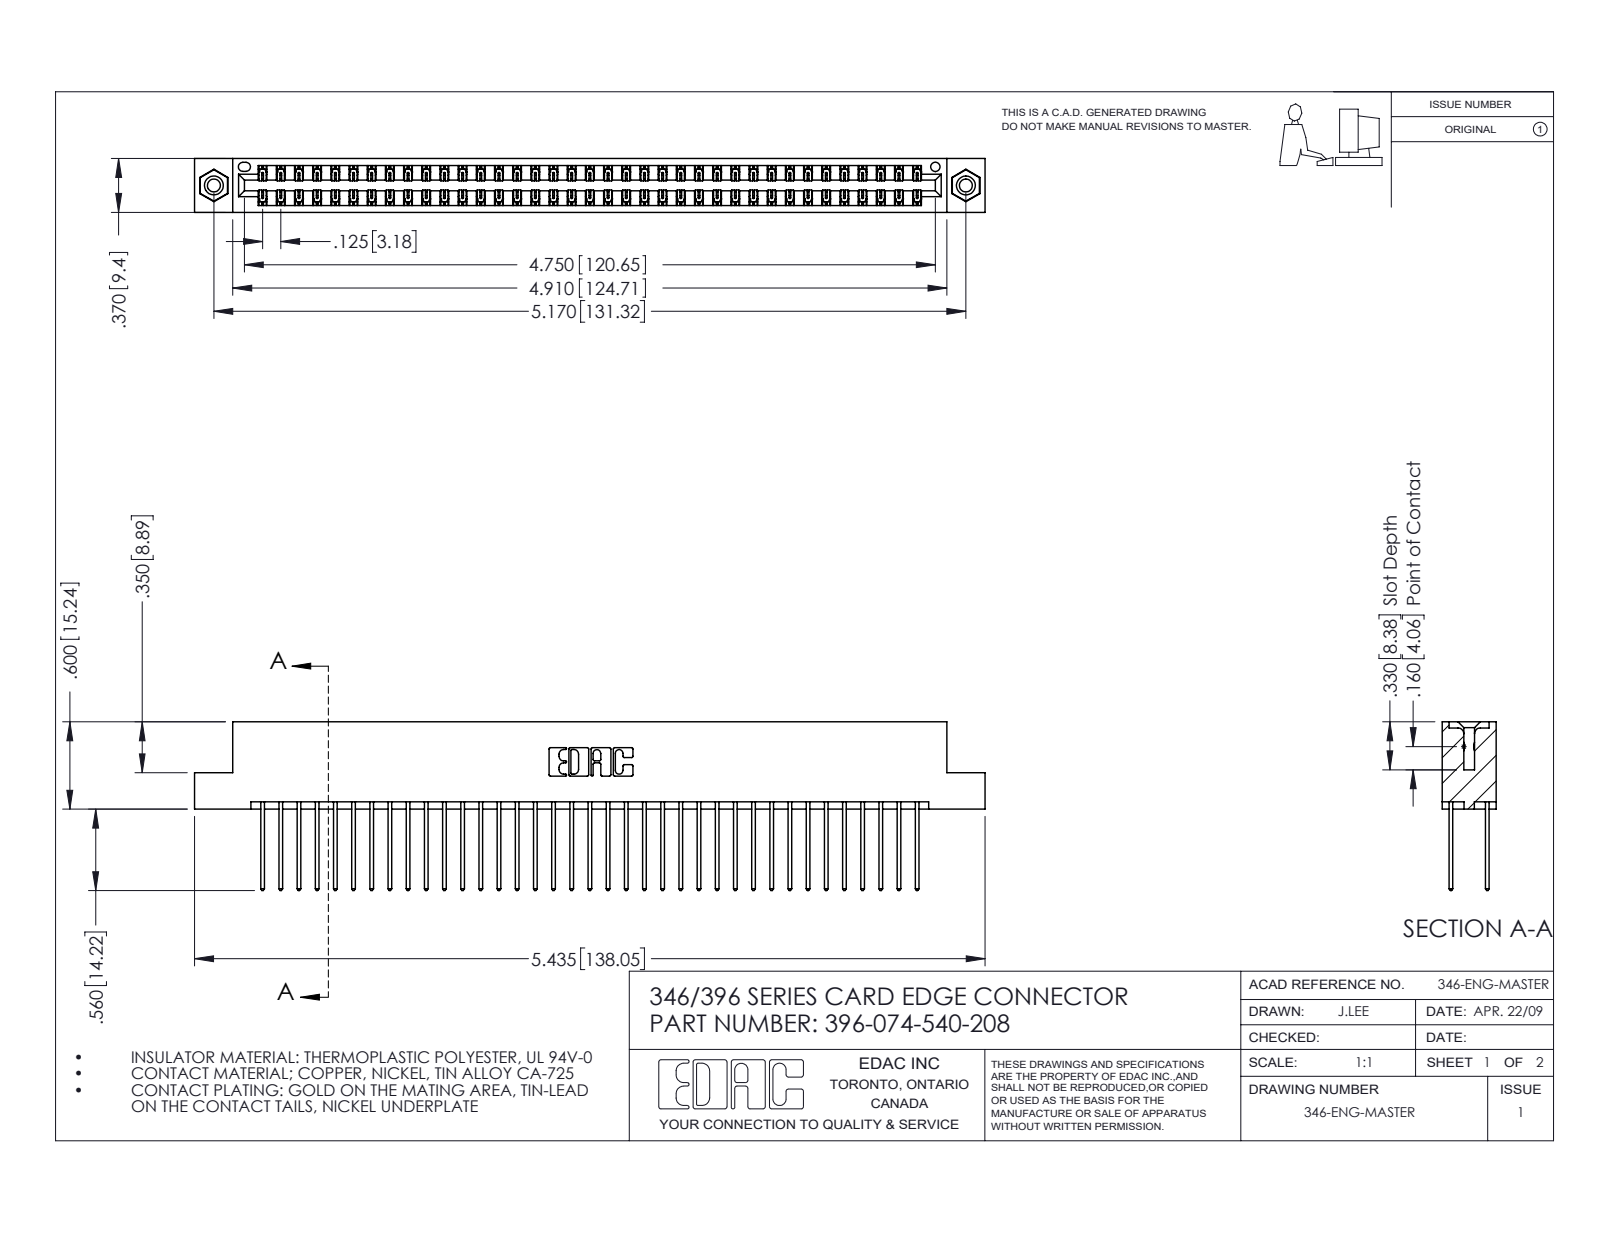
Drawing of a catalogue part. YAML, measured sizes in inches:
part_name: "345-250-001_345-250-003-102; 345-292-001_345-293-140; 396-074-540-208; 346 Part_Flush Mounting Lugs - 0.156 Dia-TI"
step_written_by: "SolidWorks 2016 (CONFIG_CONTROL_DESIGN)"
units: inches
bodies: {solids: 77, faces: 4030, planar: 2698, cylindrical: 1316, other: 16}
overall_size: [5.435, 1.16, 0.37]
volume: 0.836
surface_area: 31.15
round_holes:
  - {diameter: 0.089, count: 2}
  - {diameter: 0.125, count: 2}
  - {diameter: 0.156, count: 2}
  - {diameter: 0.064, count: 1}
round_bosses_or_shafts:
  - {diameter: 0.155, count: 2}
partial_cylinders:
  - {radius: 0.006, count: 111}
  - {radius: 0.01, count: 74}
  - {radius: 0.01, count: 22}
  - {radius: 0.007, count: 6}
  - {radius: 0.031, count: 6}
  - {radius: 0.026, count: 3}
  - {radius: 0.014, count: 2}
  - {radius: 0.022, count: 2}
face_to_face_distances: [0.048, 0.322, 0.25, 0.072, 0.298, 0.025, 0.37, 0.275, 0.148, 0.222]
hole_center_spacings: [0.246, 4.961, 5.17]
